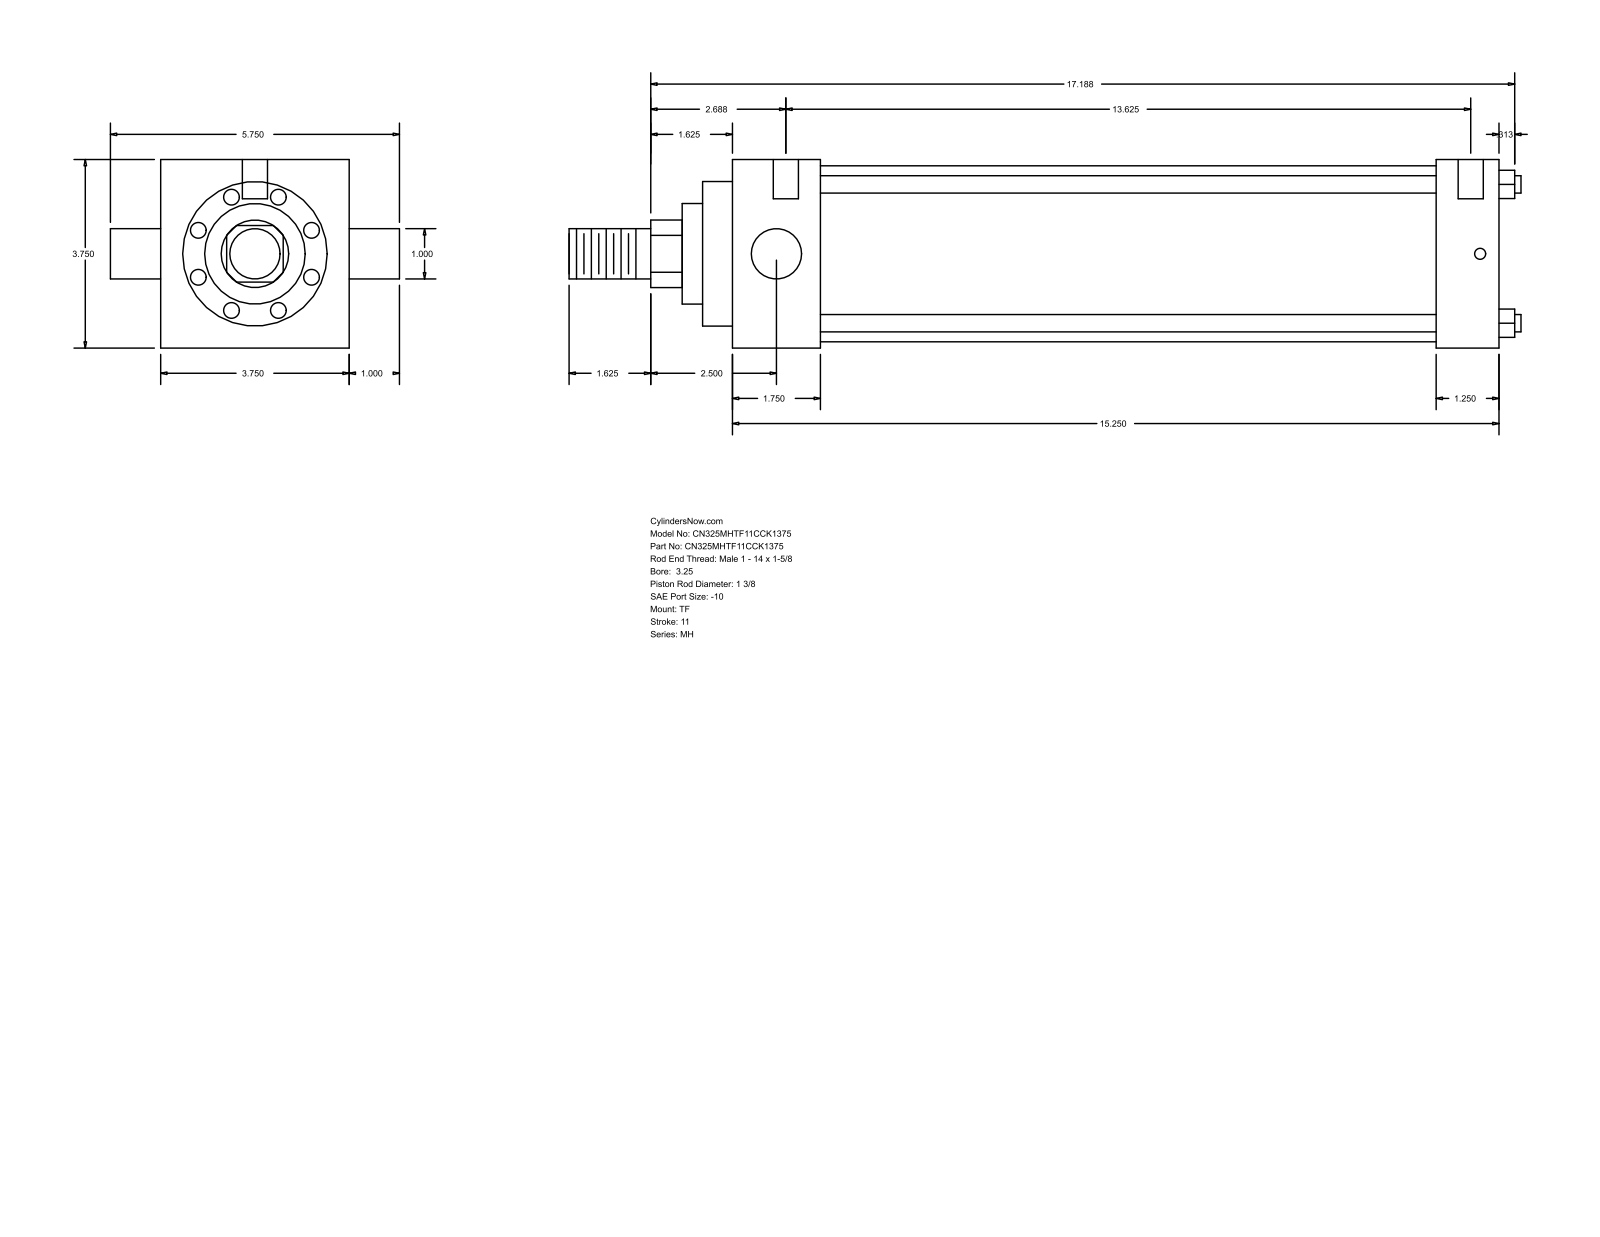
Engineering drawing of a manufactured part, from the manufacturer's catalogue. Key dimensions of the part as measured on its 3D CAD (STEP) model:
Part name (STEP PRODUCT): MH_TF__0325_1.375
STEP written by: GSSL Pune (CONFIG_CONTROL_DESIGN)
Units: millimetres
Bodies: 0 solids, 86 faces (61 planar, 25 cylindrical, 0 other)
Overall size (bounding box): 481.01 × 146.05 × 95.25
Round holes (diameter × count): ⌀5.56 ×3, ⌀12.7 ×2
Round bosses / shafts (diameter × count): ⌀8.76 ×4, ⌀25.4 ×2, ⌀88.9 ×1, ⌀73.03 ×1, ⌀50.8 ×1, ⌀34.92 ×1
Partial cylindrical surfaces — rounded edges, fillets, slot ends (radius × count): R17.06 ×1
Main face-to-face distances: 95.24, 387.35, 44.45, 355.61, 311.16, 342.9, 31.74, 15.08, 59.53, 370.69
Hole centre spacings: 1.59, 4.76, 346.08, 347.67, 350.84, 352.43
